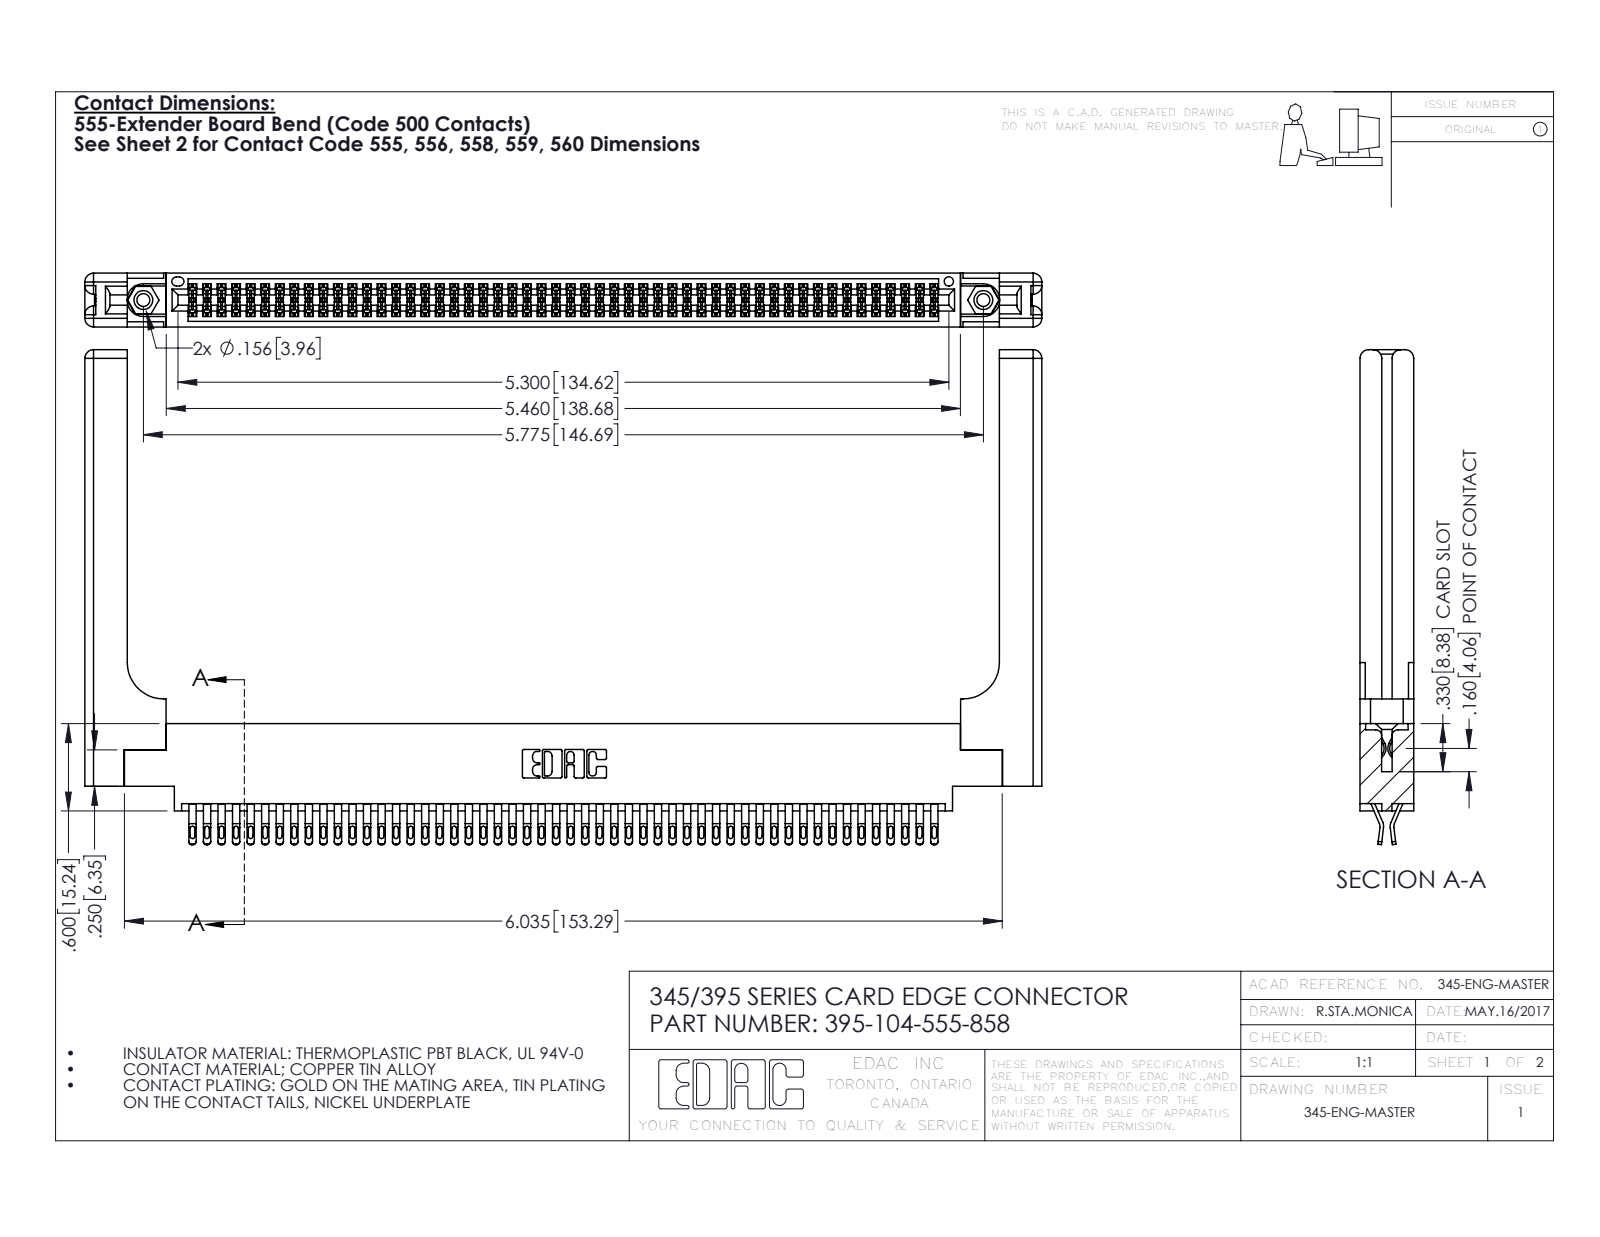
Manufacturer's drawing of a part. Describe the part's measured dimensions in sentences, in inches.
The part is named "345-220-058_345-220-058; 395-104-555-858; 345 Part_0.170 Offset - 0.156 Dia-TH; 345-250-001_345-250-001-102 (+1 more)". Its 3-D file was written by "SolidWorks 2016 (CONFIG_CONTROL_DESIGN)". It is 109 solids with 6210 faces: 3456 planar, 2694 cylindrical and 60 other. Overall it measures 6.579 by 3.402 by 0.37 inches. Its volume is 1.525 cubic inches and its surface area 47.83 square inches. Round holes: 2 of diameter 0.089, 2 of diameter 0.125, 2 of diameter 0.156, 1 of diameter 0.064. Round bosses or shafts: 2 of diameter 0.155. Partial cylindrical surfaces (rounded edges, fillets, slot ends): 260 of radius 0.016, 208 of radius 0.02, 156 of radius 0.006, 22 of radius 0.01, 16 of radius 0.06, 6 of radius 0.007, 6 of radius 0.031, 3 of radius 0.026. The main face-to-face distances are 0.072, 0.37, 0.298, 0.025, 0.098, 0.272, 0.2, 0.225, 0.175, 0.148. The hole center spacings are 0.27, 5.539, 5.775.
